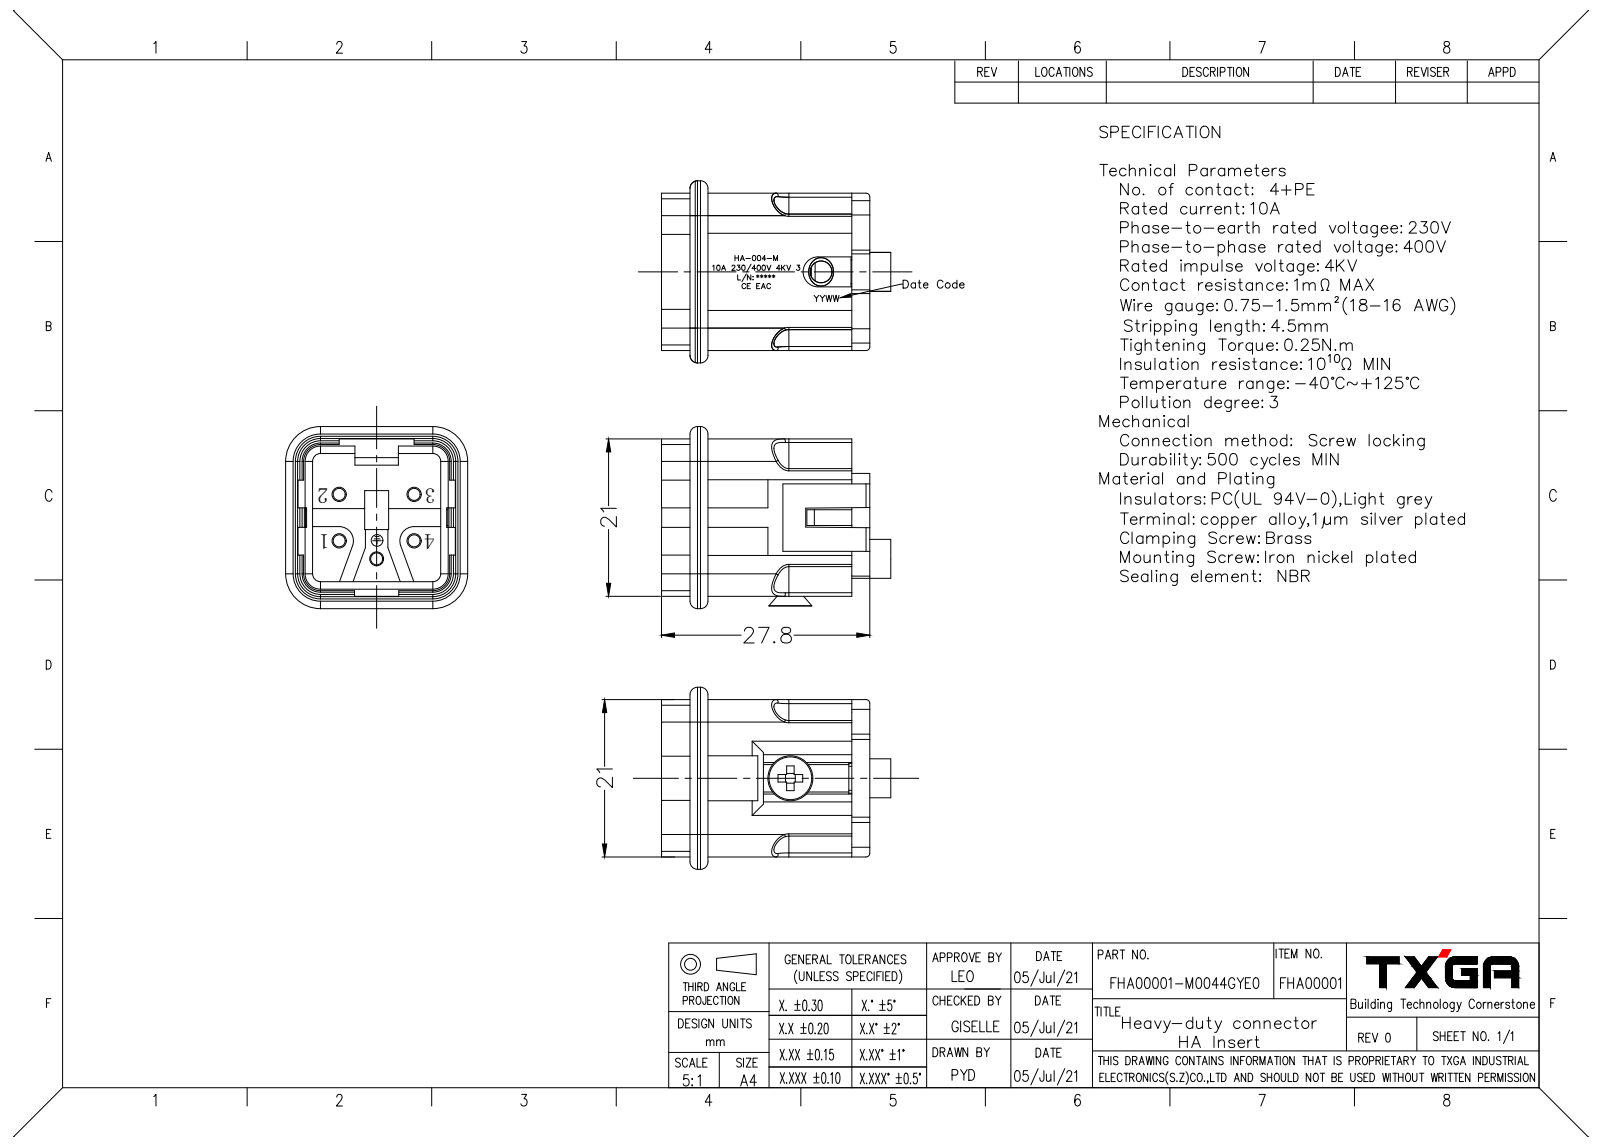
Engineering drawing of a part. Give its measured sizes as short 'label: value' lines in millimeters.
name: FHA00001-M0044GYE0 HA-004-M
written by: SolidWorks 2021 (CONFIG_CONTROL_DESIGN)
unit: mm
bodies: 1 solid, 788 faces (446 planar, 227 cylindrical, 115 other)
size: 30.6 × 24.3 × 24.3
volume: 6 126 mm³; area: 8 213 mm²
holes: 5× ⌀3.3, 5× ⌀3.5, 4× ⌀1.9, 4× ⌀2.8, 4× ⌀4.7, 3× ⌀2.5, 2× ⌀2.25, 1× ⌀1.85, 1× ⌀2.9, 1× ⌀3
bosses: 5× ⌀3.2, 5× ⌀1.6, 4× ⌀4.5, 4× ⌀2.9, 2× ⌀2, 1× ⌀5.7, 1× ⌀5.2, 1× ⌀3.1
rounds: 40× R0.15, 32× R0.3, 16× R0.2, 15× R1, 7× R2, 4× R0.5, 4× R1.05, 4× R2.25
face distances: 1.95, 19.05, 18.3, 20.25, 0.75, 1.2, 0.8, 0.4, 17.9, 21
hole spacings: 3.98, 12.88, 4.32, 5.55, 6.2, 9.3, 9.95, 10
